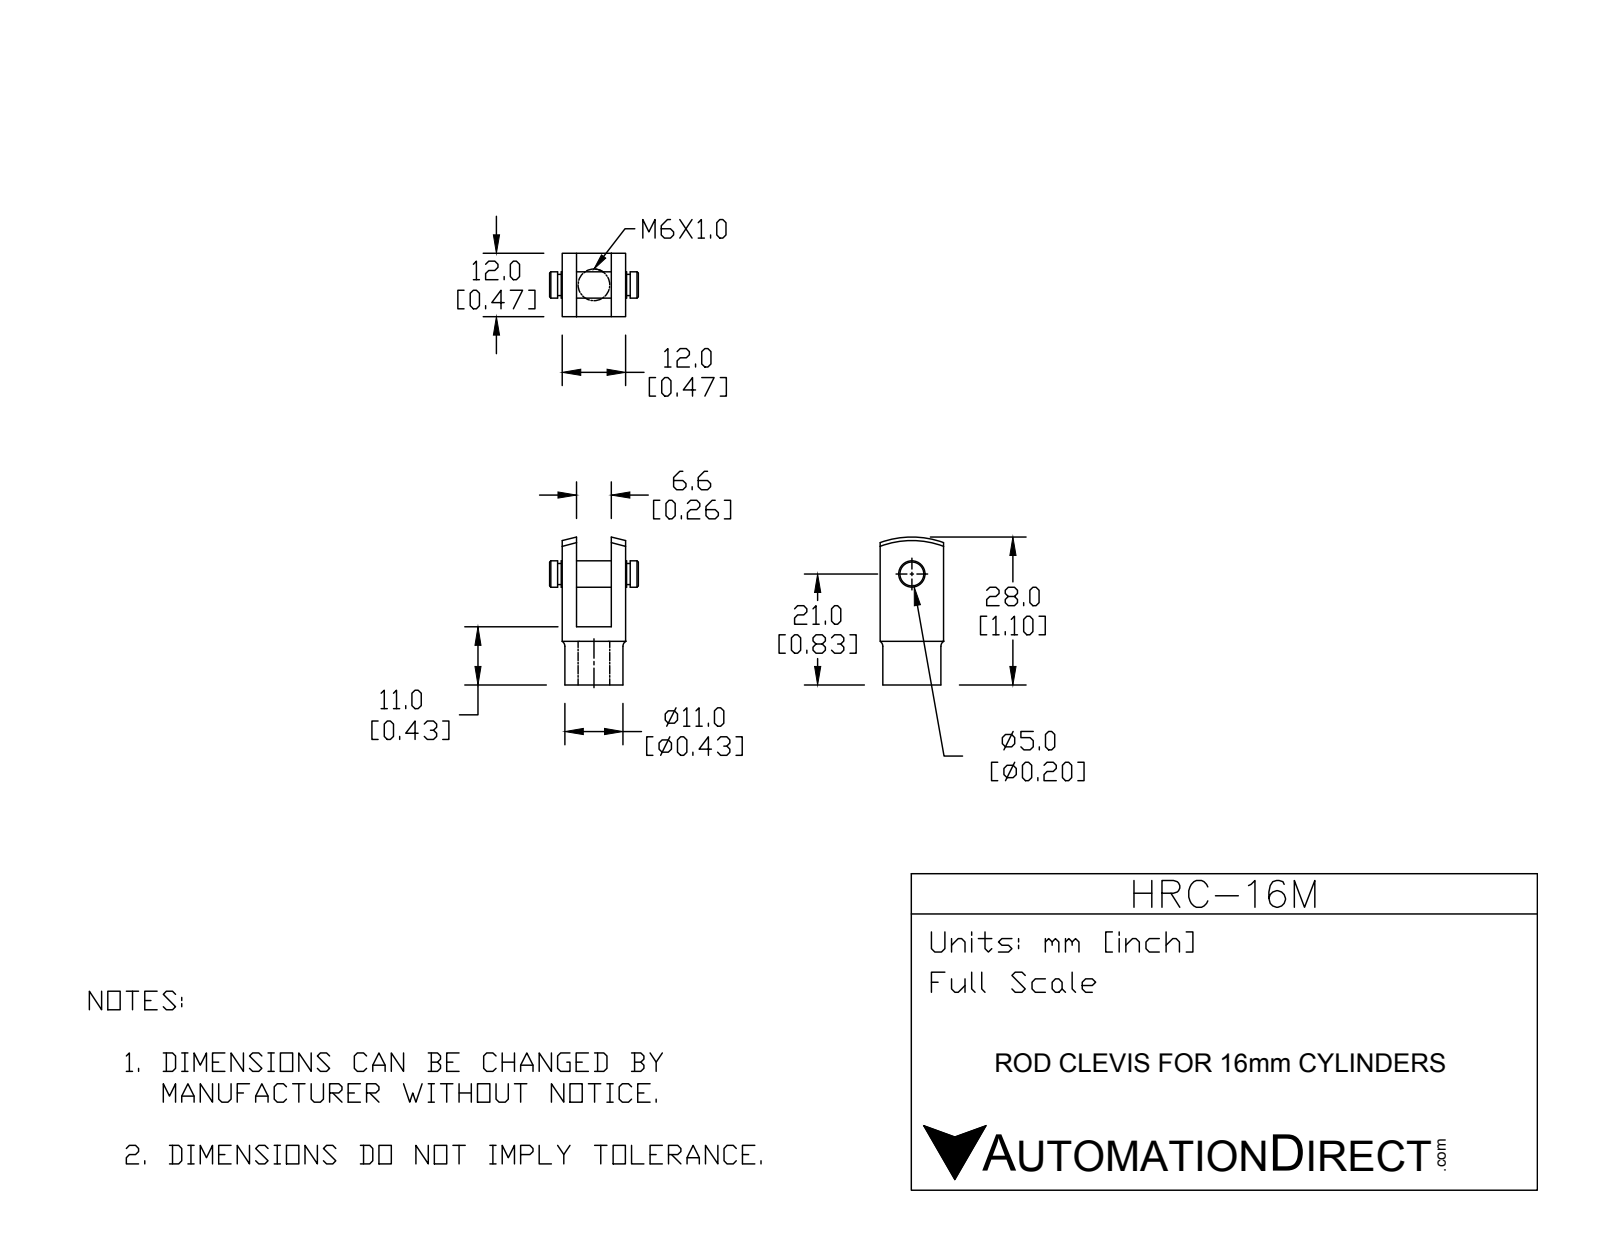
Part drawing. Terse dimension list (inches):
name: HRC-16M
written by: SolidWorks 2015 (CONFIG_CONTROL_DESIGN)
unit: in
bodies: 2 solids, 54 faces (18 planar, 18 cylindrical, 18 other)
size: 1.102 × 0.661 × 0.472
volume: 0.137 in³; area: 3.253 in²
holes: 1× ⌀0.197
bosses: 1× ⌀0.433, 1× ⌀0.197, 1× ⌀0.157
face distances: 0.106, 0.366, 0.472, 0.26, 0.433, 0.094, 0.201, 0.461, 0.567, 0.325
